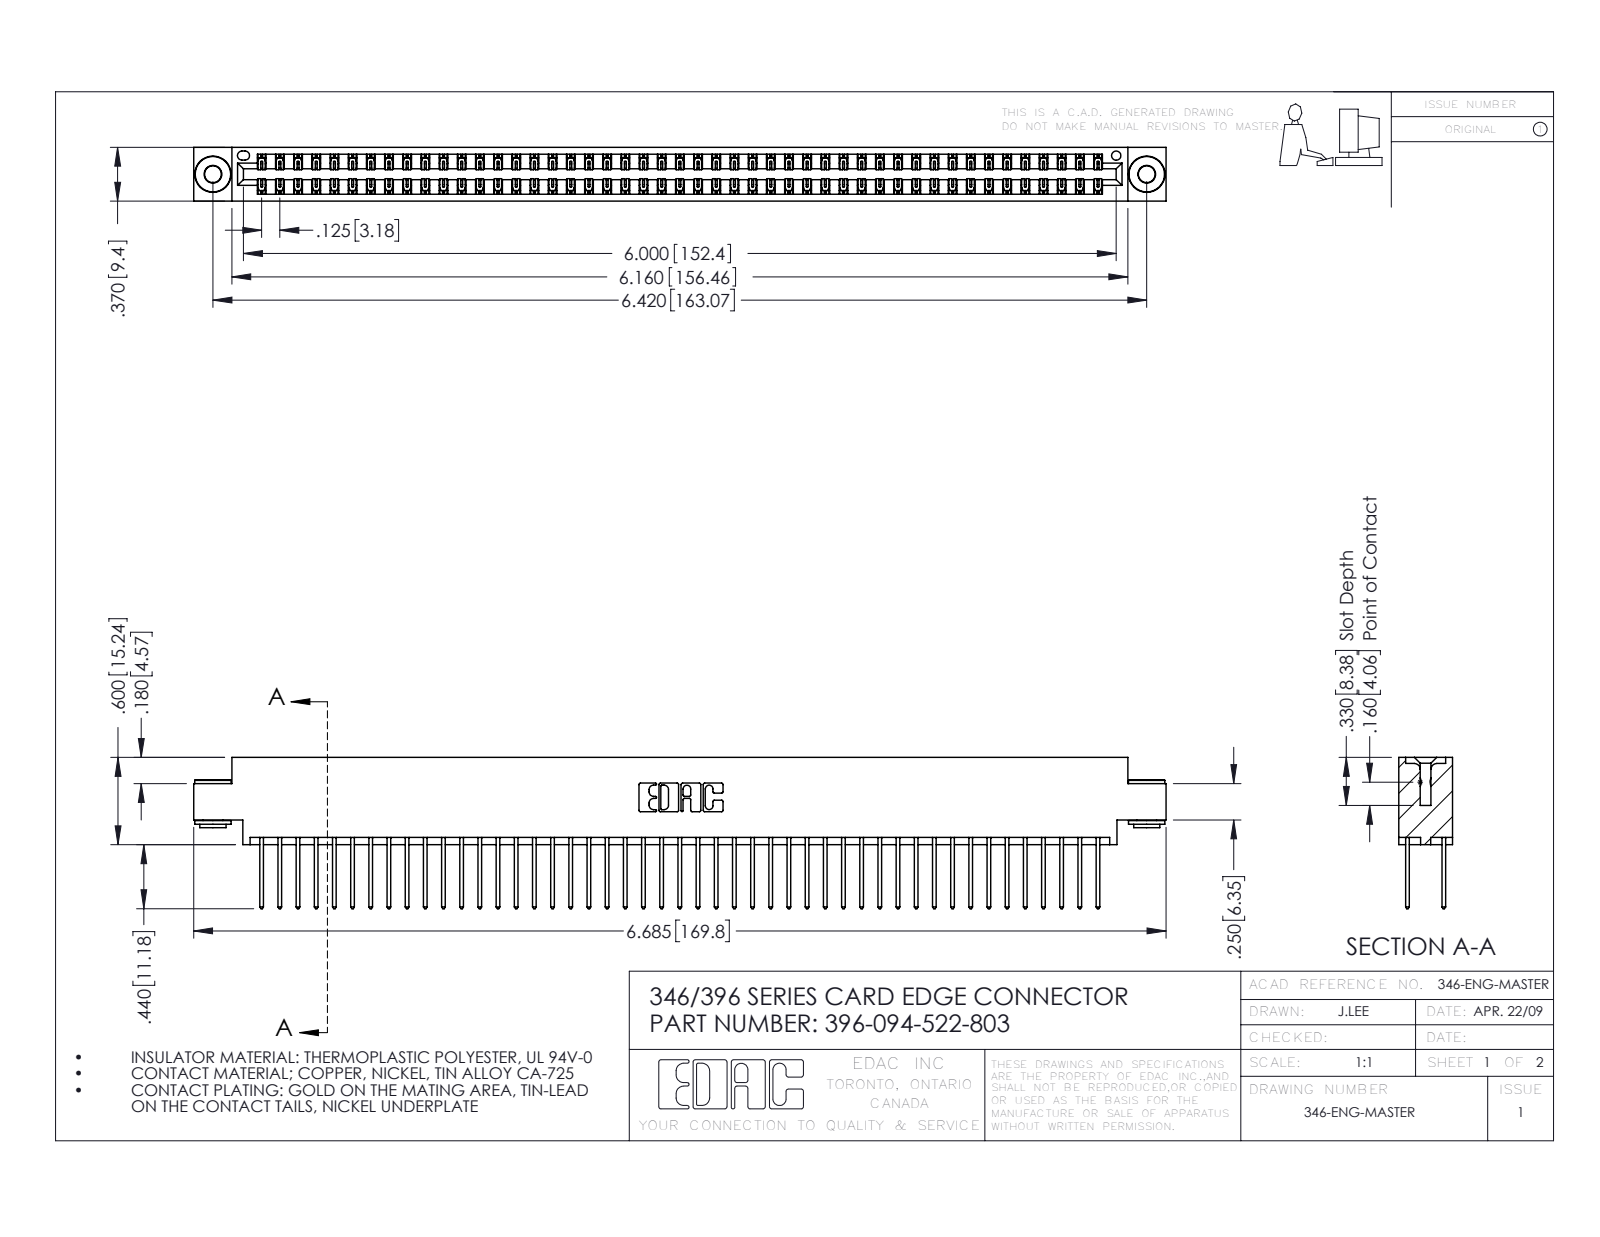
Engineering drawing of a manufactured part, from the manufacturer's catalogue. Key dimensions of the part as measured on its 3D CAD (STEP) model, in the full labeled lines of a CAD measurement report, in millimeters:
Part name (STEP PRODUCT): 345-292-001_345-293-122; 345-250-002_345-250-002-102; 396-094-522-803; 346 Part_0.170 Offset - 0.156 Dia-TH
STEP written by: SolidWorks 2016 (CONFIG_CONTROL_DESIGN)
Units: millimetres
Bodies: 97 solids, 5052 faces (3380 planar, 1664 cylindrical, 8 other)
Overall size (bounding box): 169.8 × 26.4 × 9.4
Volume: 16 700 mm³ · Surface area: 24 550 mm²
Round holes (diameter × count): ⌀2.9 ×2, ⌀4 ×2, ⌀1.6 ×1
Round bosses / shafts (diameter × count): ⌀6.4 ×2, ⌀4.6 ×2, ⌀3.5 ×2
Partial cylindrical surfaces — rounded edges, fillets, slot ends (radius × count): R0.2 ×141, R0.3 ×94, R0.3 ×22, R0.2 ×6, R0.8 ×6, R0.7 ×3, R0.4 ×2, R0.6 ×2
Main face-to-face distances: 1.2, 8.2, 6.4, 9.4, 0.6, 1.8, 7.6, 7, 3.8, 5.6
Hole centre spacings: 6.2, 157.8, 163.1
